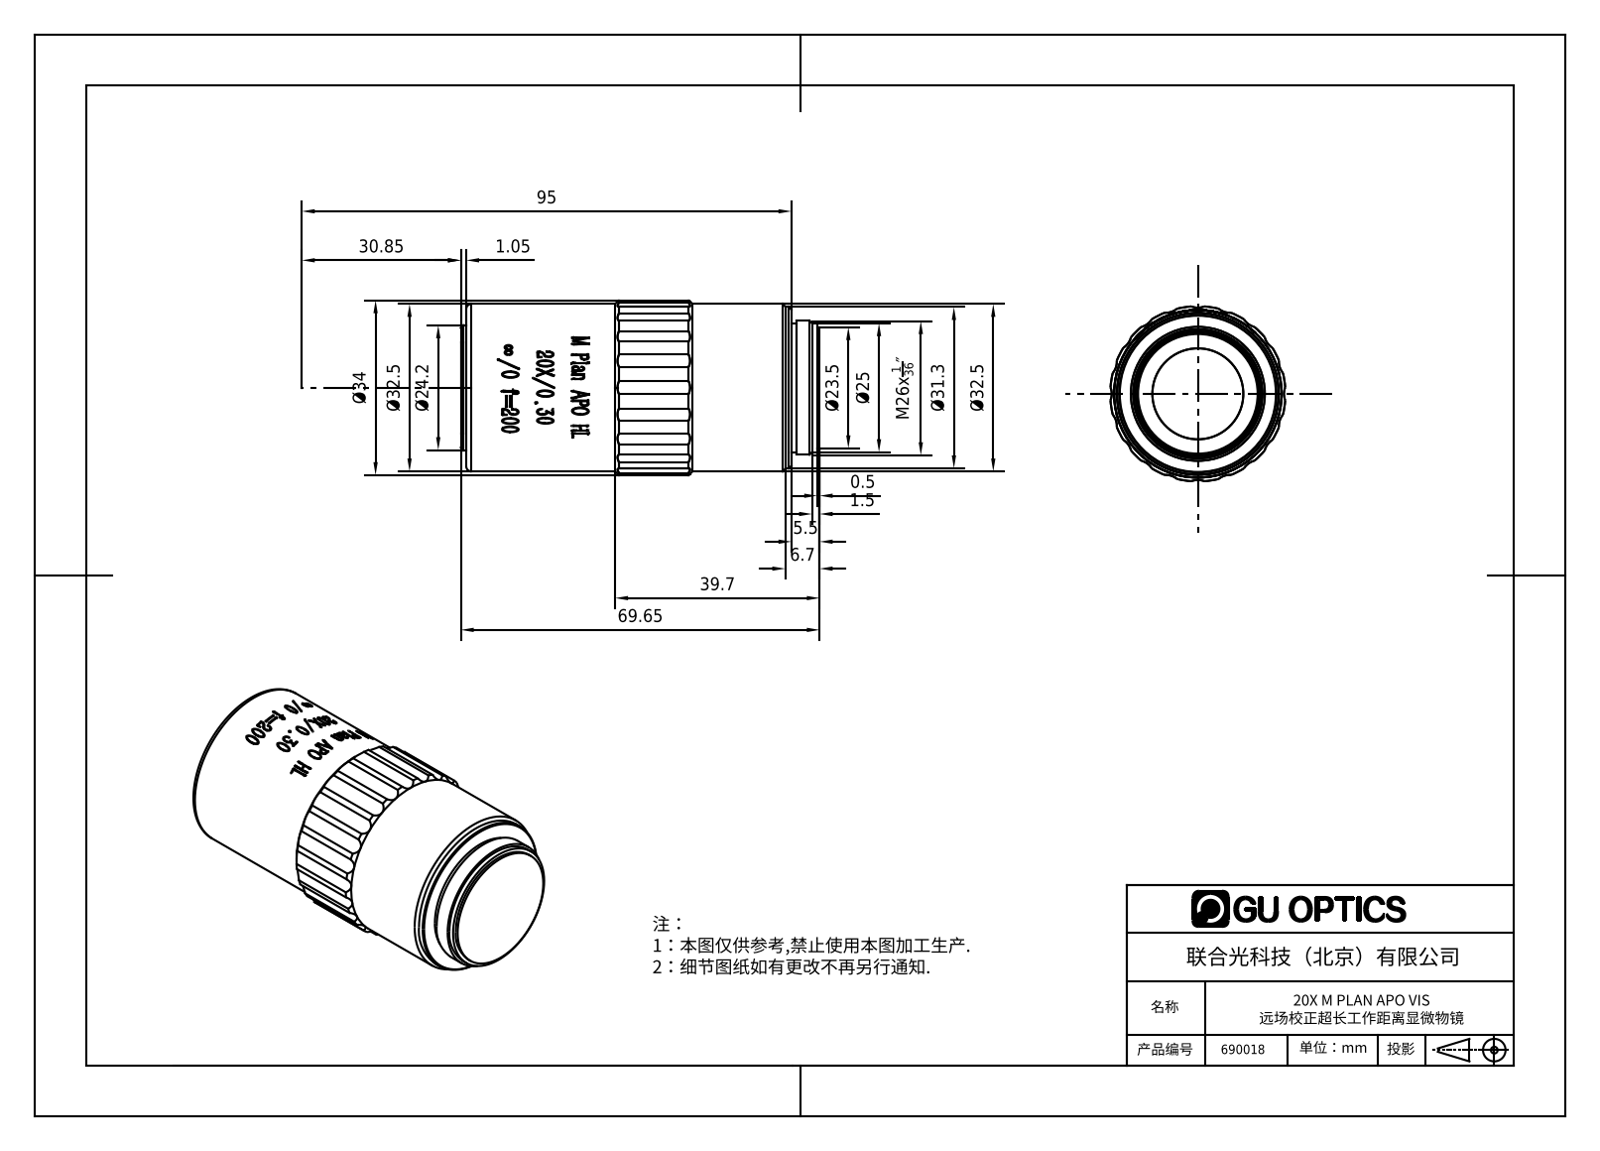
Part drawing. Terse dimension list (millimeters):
name: 690018带树
written by: SolidWorks 2020 (AUTOMOTIVE_DESIGN)
unit: mm
bodies: 1 solid, 611 faces (46 planar, 115 cylindrical, 450 other)
size: 69.85 × 33.99 × 33.93
volume: 55 762 mm³; area: 9 066 mm²
holes: 1× ⌀22
bosses: 1× ⌀32.5, 1× ⌀31.3, 1× ⌀26, 1× ⌀25, 1× ⌀24.2, 1× ⌀23.5
rounds: 25× R2, 1× R15.75, 1× R17
face distances: 68.85, 68.6, 63.35, 63.1, 5.5, 1, 68.35, 64.35, 4, 68.1
